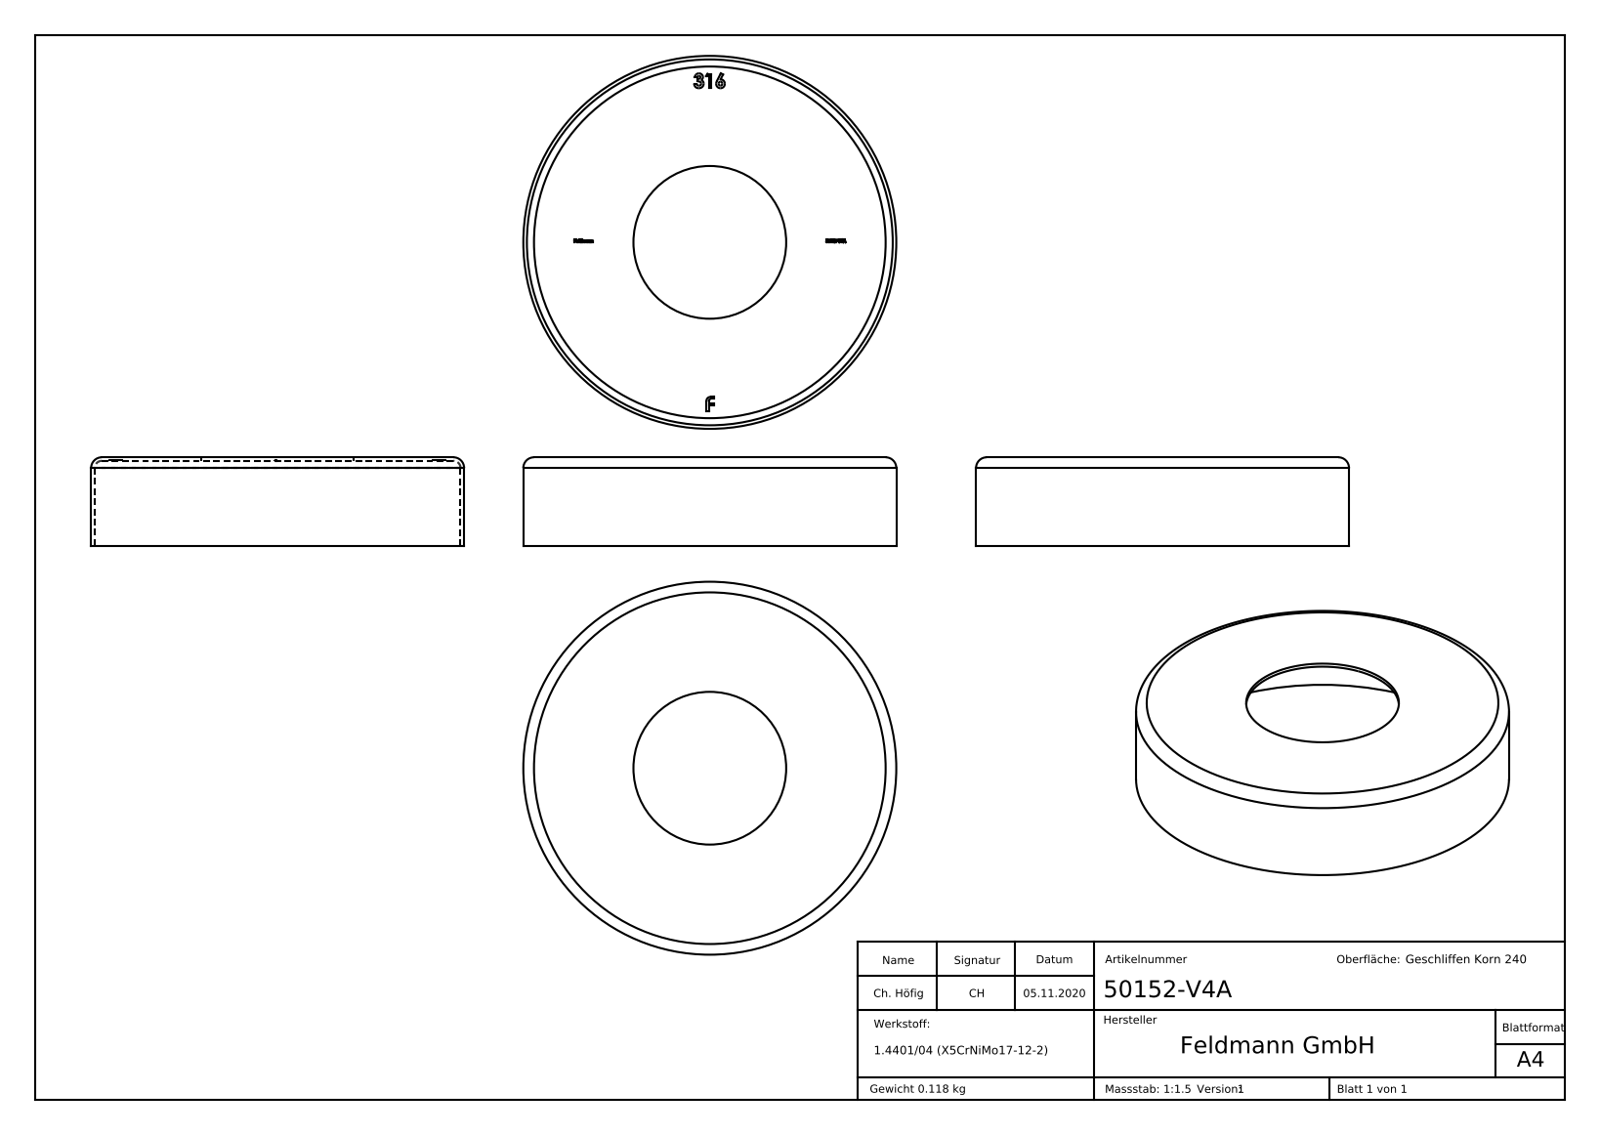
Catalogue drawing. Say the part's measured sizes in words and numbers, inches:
The part is named "50152-V4A". Its 3-D file was written by "SolidWorks 2018 (CONFIG_CONTROL_DESIGN)". It is 1 solid with 278 faces: 166 planar, 6 cylindrical and 106 other. Overall it measures 4.134 by 4.134 by 0.984 inches. Its volume is 0.897 cubic inches and its surface area 46.29 square inches. Round holes: 1 of diameter 1.693, 1 of diameter 4.055. Round bosses or shafts: 1 of diameter 4.134. The main face-to-face distances are 0.039, 0.945, 0.984, 0.949, 0.035, 0.028, 0.029, 0.057, 0.03, 1.812.
